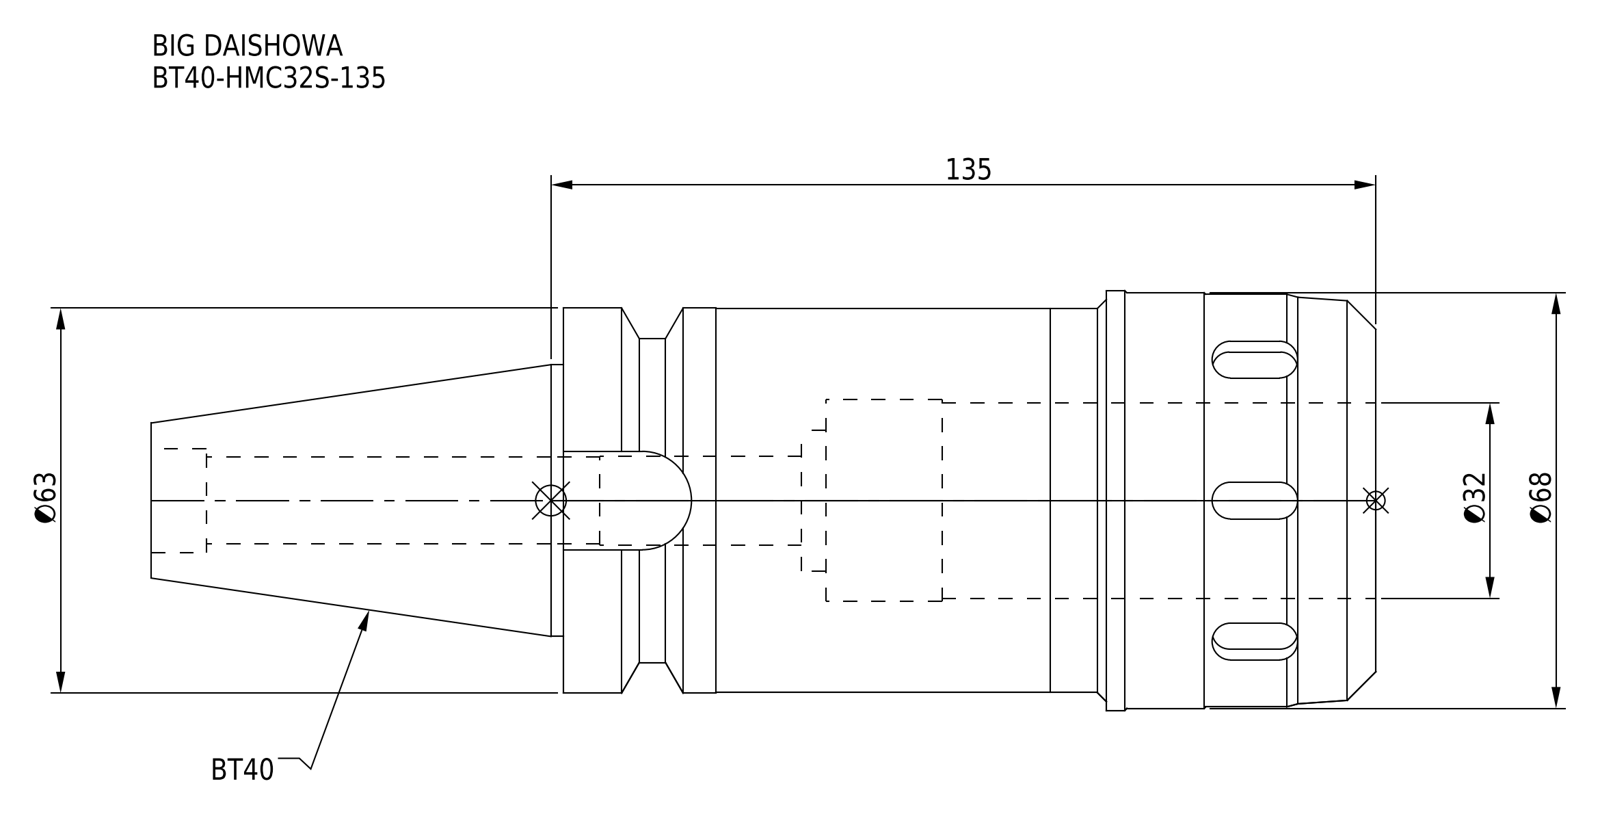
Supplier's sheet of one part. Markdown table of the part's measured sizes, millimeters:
| quantity | value |
| --- | --- |
| part name | BT40-HMC32S-135 |
| STEP written by | CREO PARAMETRIC BY PTC INC, 2016380 (AUTOMOTIVE_DESIGN) |
| units | millimeters |
| bodies | 1 solid, 104 faces (40 planar, 46 cylindrical, 18 other) |
| overall size | 200.4 × 68.7 × 68.7 |
| volume | 392 704 mm³ |
| surface area | 55 435 mm² |
| round holes (diameter × count) | 14.2 × 1, 14.5 × 1, 17 × 1, 23 × 1, 32 × 1, 33 × 1 |
| round bosses / shafts (diameter × count) | 68.7 × 1, 68 × 1, 67.5 × 1, 63 × 1, 62.8 × 1, 53 × 1, 44.45 × 1 |
| partial cylindrical surfaces (radius × count) | 3 × 12, 8.05 × 1 |
| main face-to-face distances | 133, 90, 43, 45, 44.1, 45.9, 88.9, 63, 200.4, 156.3 |
